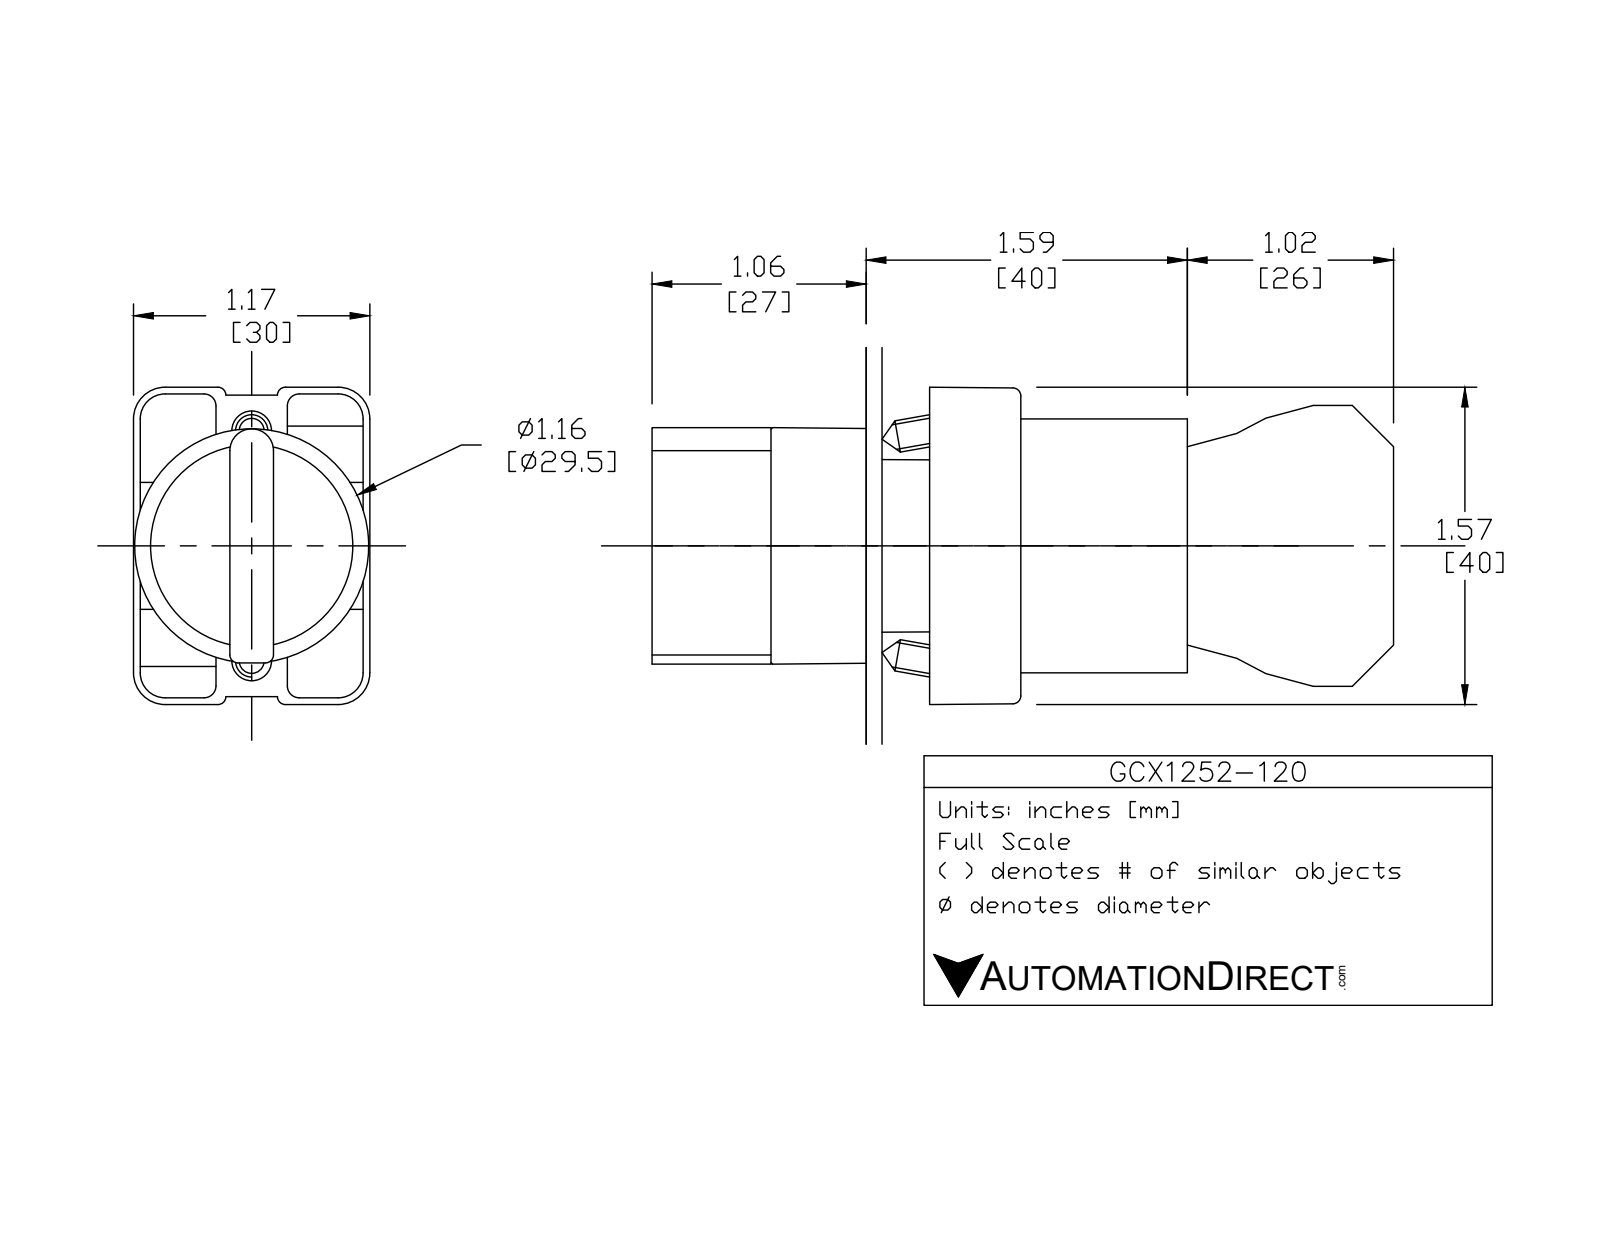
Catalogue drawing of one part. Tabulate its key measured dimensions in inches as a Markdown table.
| quantity | value |
| --- | --- |
| part name | GCX1252 OPERATOR; ECX1050; ecx1029; GCX1252-120 (+1 more) |
| STEP written by | SolidWorks 2016 (AUTOMOTIVE_DESIGN) |
| units | inches |
| bodies | 8 solids, 445 faces (263 planar, 151 cylindrical, 31 other) |
| overall size | 3.653 × 1.581 × 1.177 |
| volume | 2.799 in³ |
| surface area | 39 in² |
| round holes (diameter × count) | 0.079 × 2, 0.124 × 2, 0.13 × 2, 0.087 × 1, 0.197 × 1, 0.469 × 1, 0.878 × 1, 0.888 × 1, 1.024 × 1 |
| round bosses / shafts (diameter × count) | 0.157 × 4, 1.175 × 1, 1.004 × 1, 0.945 × 1, 0.856 × 1, 0.78 × 1, 0.504 × 1 |
| partial cylindrical surfaces (radius × count) | 0.059 × 24, 0.041 × 12, 0.124 × 12, 0.157 × 12, 0.039 × 9, 0.128 × 2, 0.02 × 1, 0.063 × 1 |
| main face-to-face distances | 0.827, 2.02, 1.193, 0.579, 1.244, 1.171, 0.472, 0.469, 0.031, 0.033 |
| hole center spacings | 0.236, 0.544, 0.472, 0.49 |
